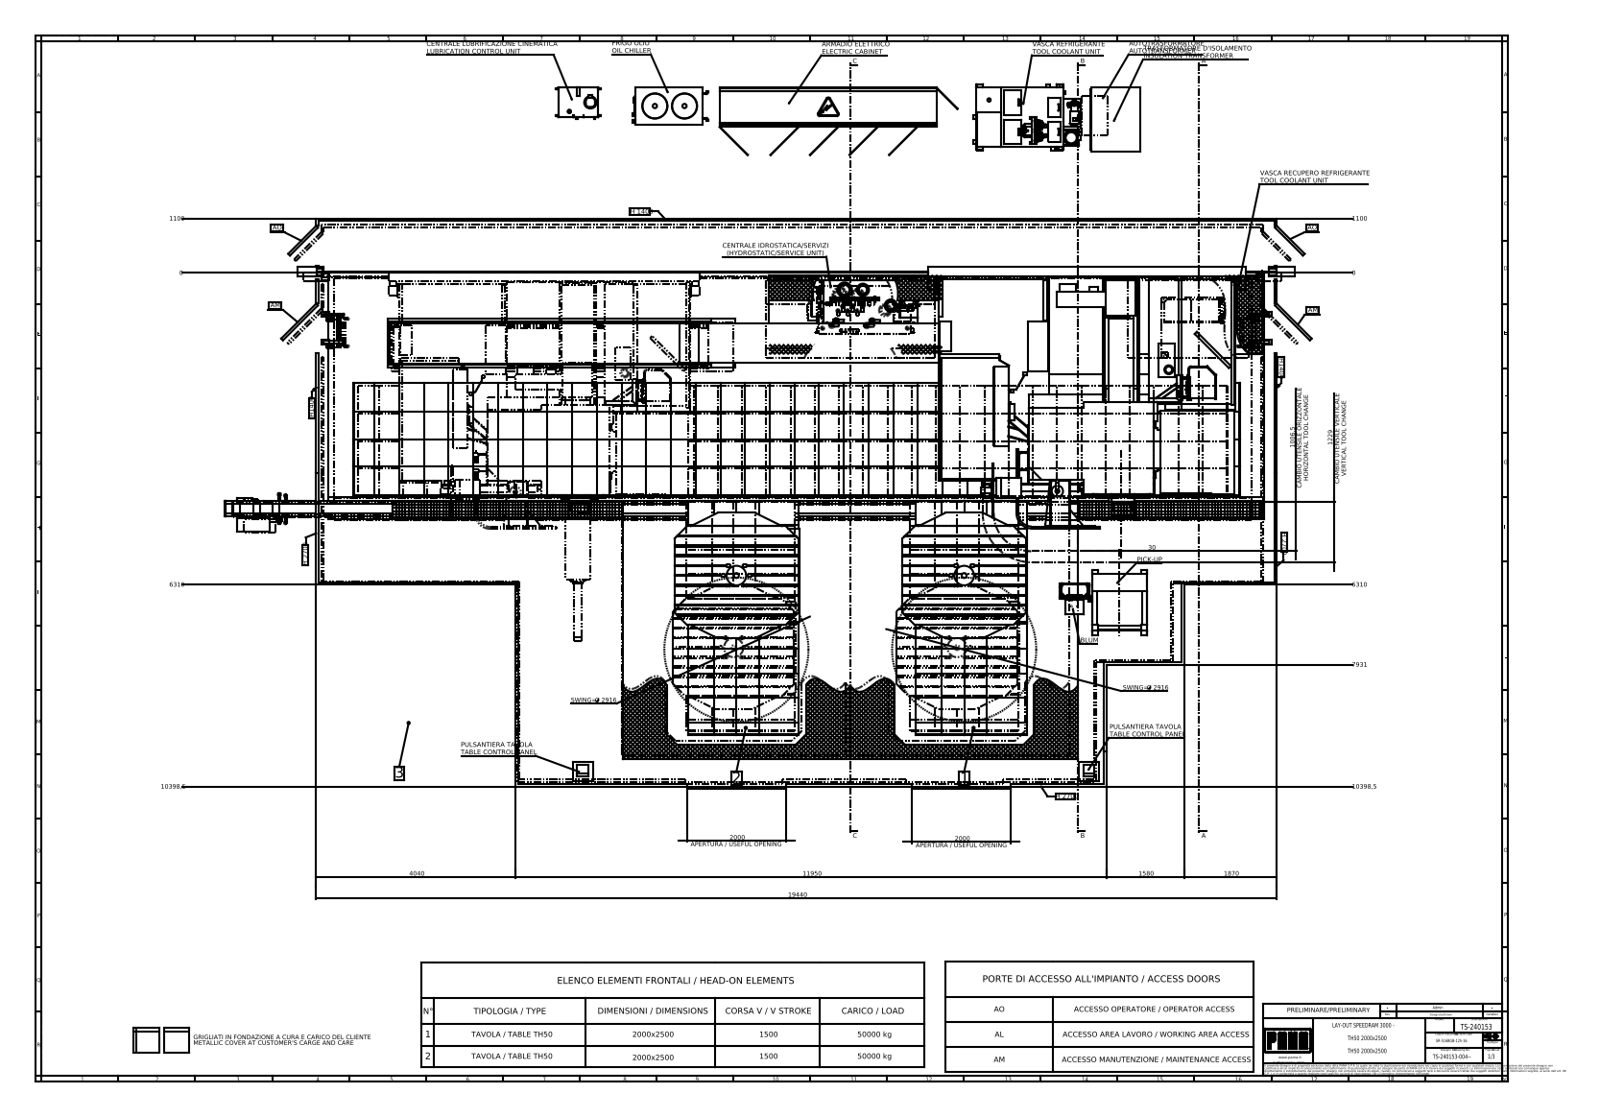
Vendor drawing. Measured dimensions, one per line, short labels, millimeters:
name: S001571; S003244_SRAM 6-516; S003214_Y=4000; S001568_1000 L (+8 more)
written by: SolidWorks 2023 (AUTOMOTIVE_DESIGN)
unit: mm
bodies: 526 solids, 8918 faces (6181 planar, 2163 cylindrical, 574 other)
size: 22940 × 17169.9 × 10174
volume: 679 300 000 000 mm³; area: 2 539 000 000 mm²
holes: 172× ⌀35, 103× ⌀69.6, 18× ⌀37.2, 9× ⌀30, 8× ⌀13, 8× ⌀14, 6× ⌀8, 5× ⌀340, 4× ⌀12.5, 4× ⌀56.66, 4× ⌀60, 3× ⌀25.6
bosses: 18× ⌀42.4, 14× ⌀20, 11× ⌀150, 11× ⌀40, 10× ⌀9, 9× ⌀60, 8× ⌀55, 7× ⌀66.3
rounds: 160× R5, 97× R15, 62× R35, 52× R8, 36× R10, 36× R20, 31× R6, 25× R3
face distances: 2000, 50, 720, 1280, 10, 462, 11448.5, 17098.5, 1182, 818
hole spacings: 273.13, 500, 1431.99, 758.02, 1597.06, 1000, 1254.83, 1884.3
